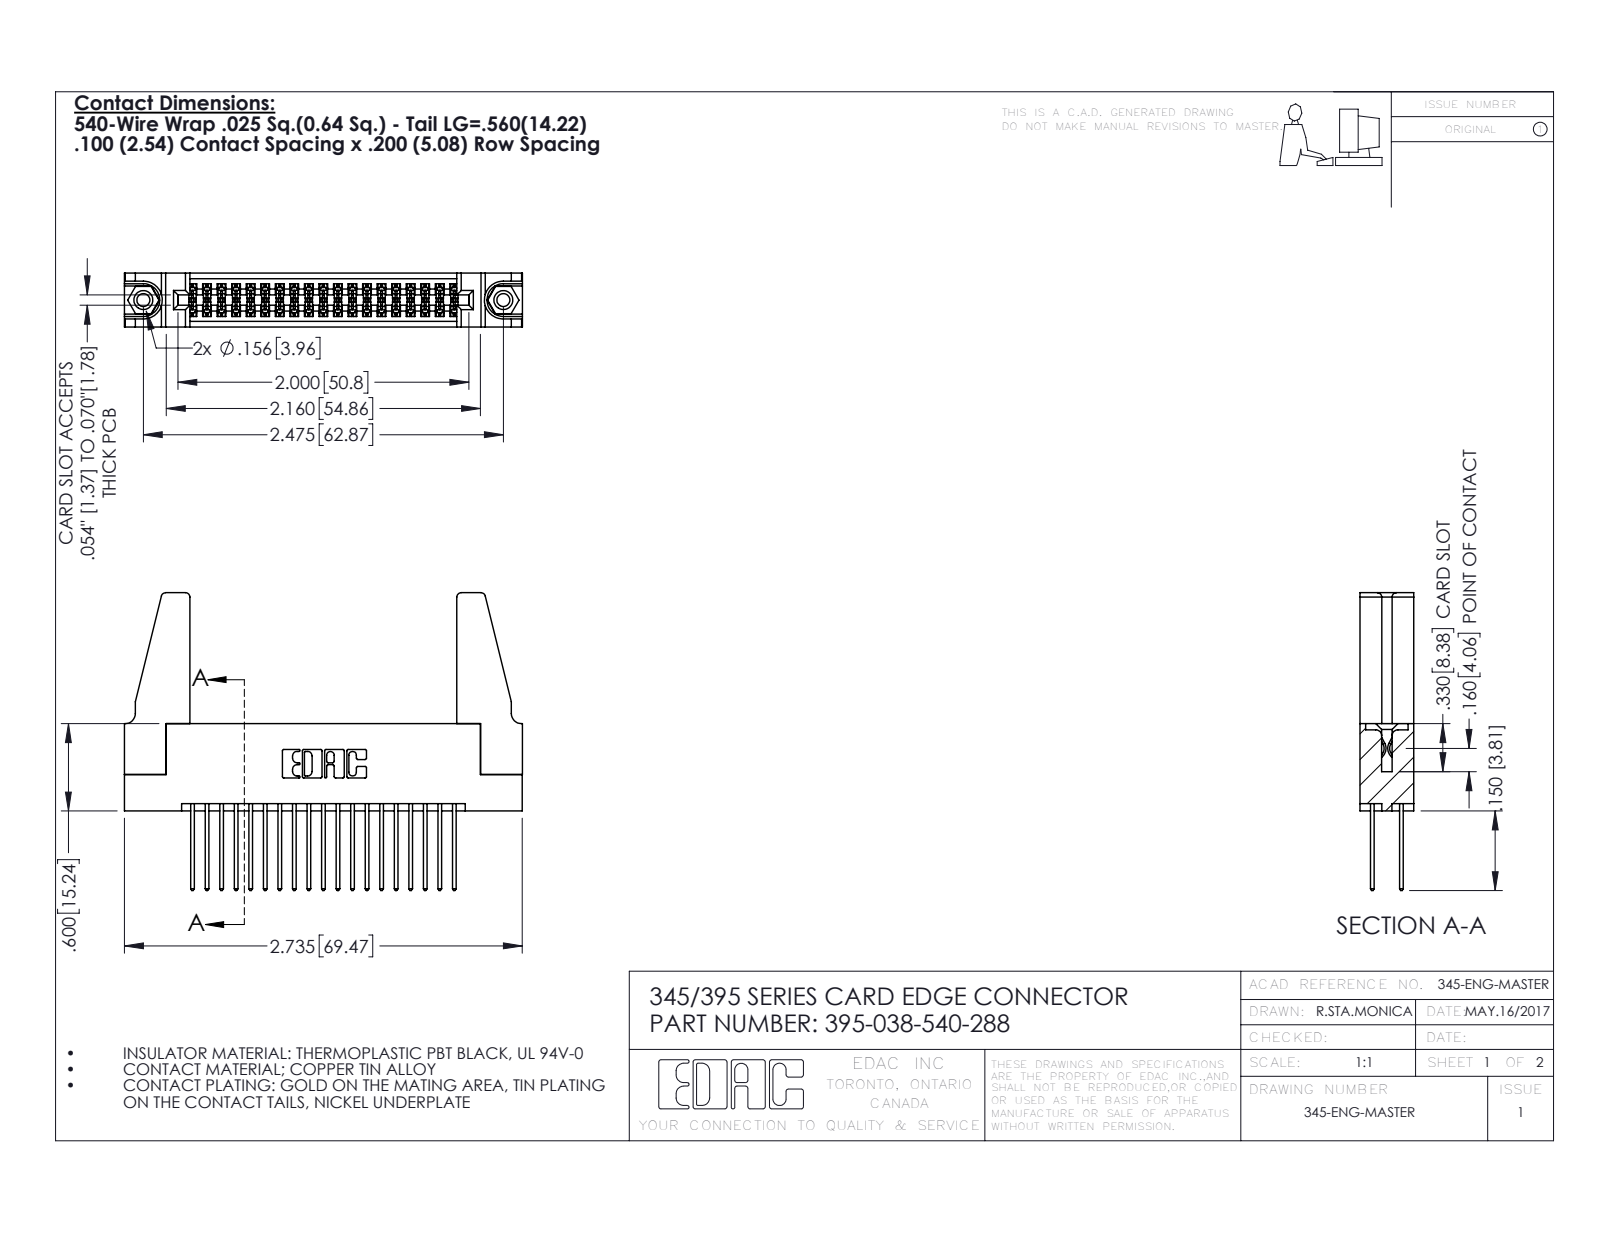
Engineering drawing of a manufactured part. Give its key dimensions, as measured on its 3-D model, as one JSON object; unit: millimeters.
{"part_name": "345-220-078_345-220-088; 395-038-540-288; 345-250-001_345-250-001-102; 345 Part_Flush Mounting Lugs - 0.156 Dia-TH (+1 more)", "step_written_by": "SolidWorks 2016 (CONFIG_CONTROL_DESIGN)", "units": "millimeters", "bodies": {"solids": 43, "faces": 2150, "planar": 1406, "cylindrical": 728, "other": 16}, "overall_size": [69.5, 52, 9.4], "volume_mm3": 9930, "surface_area_mm2": 13220, "round_holes": [[2.3, 2], [3.2, 2], [4, 2], [1.6, 1]], "round_bosses_or_shafts": [[3.9, 2]], "partial_cylinders_radius": [[0.2, 57], [0.3, 38], [0.3, 22], [0.8, 8], [0.2, 6], [0.8, 6], [0.7, 3], [0.4, 2]], "face_to_face_distances": [1.8, 7.6, 9.4, 5.1, 2.5, 6.9, 0.6, 5.7, 4.4, 3.8], "hole_center_spacings": [6.9, 56.9, 62.9]}
